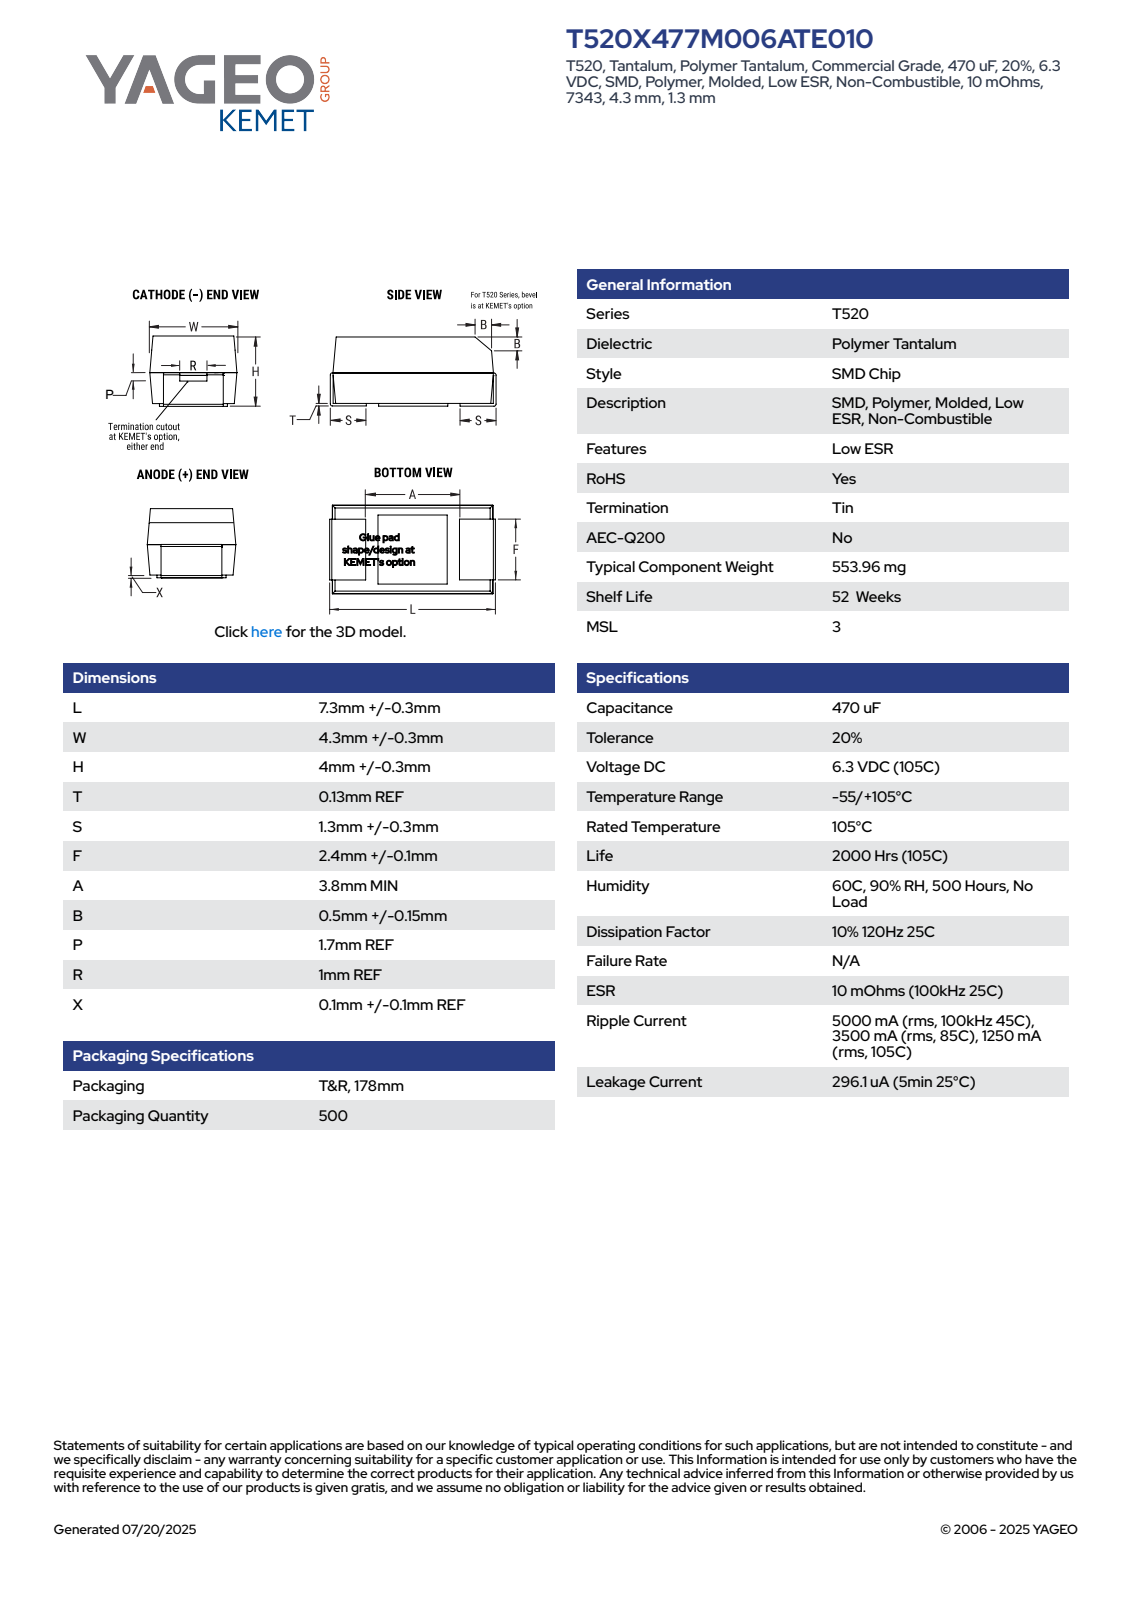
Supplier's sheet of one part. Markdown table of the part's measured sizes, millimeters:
| quantity | value |
| --- | --- |
| part name | Case_Anode_30; Case_Cathode_30; Case_Bottom_30; CTS_7343_L7.60W4.60H4.30S1.3F2.4R1P1.7B0.5 (+1 more) |
| STEP written by | SolidWorks 2014 (AUTOMOTIVE_DESIGN) |
| units | millimeters |
| bodies | 4 solids, 43 faces (38 planar, 5 cylindrical, 0 other) |
| overall size | 7.6 × 4.6 × 4.3 |
| volume | 135 mm³ |
| surface area | 257 mm² |
| main face-to-face distances | 4.58, 2.17, 2, 4.17, 7.31, 2.1, 4.27, 7.47, 2.13, 4.3 |
